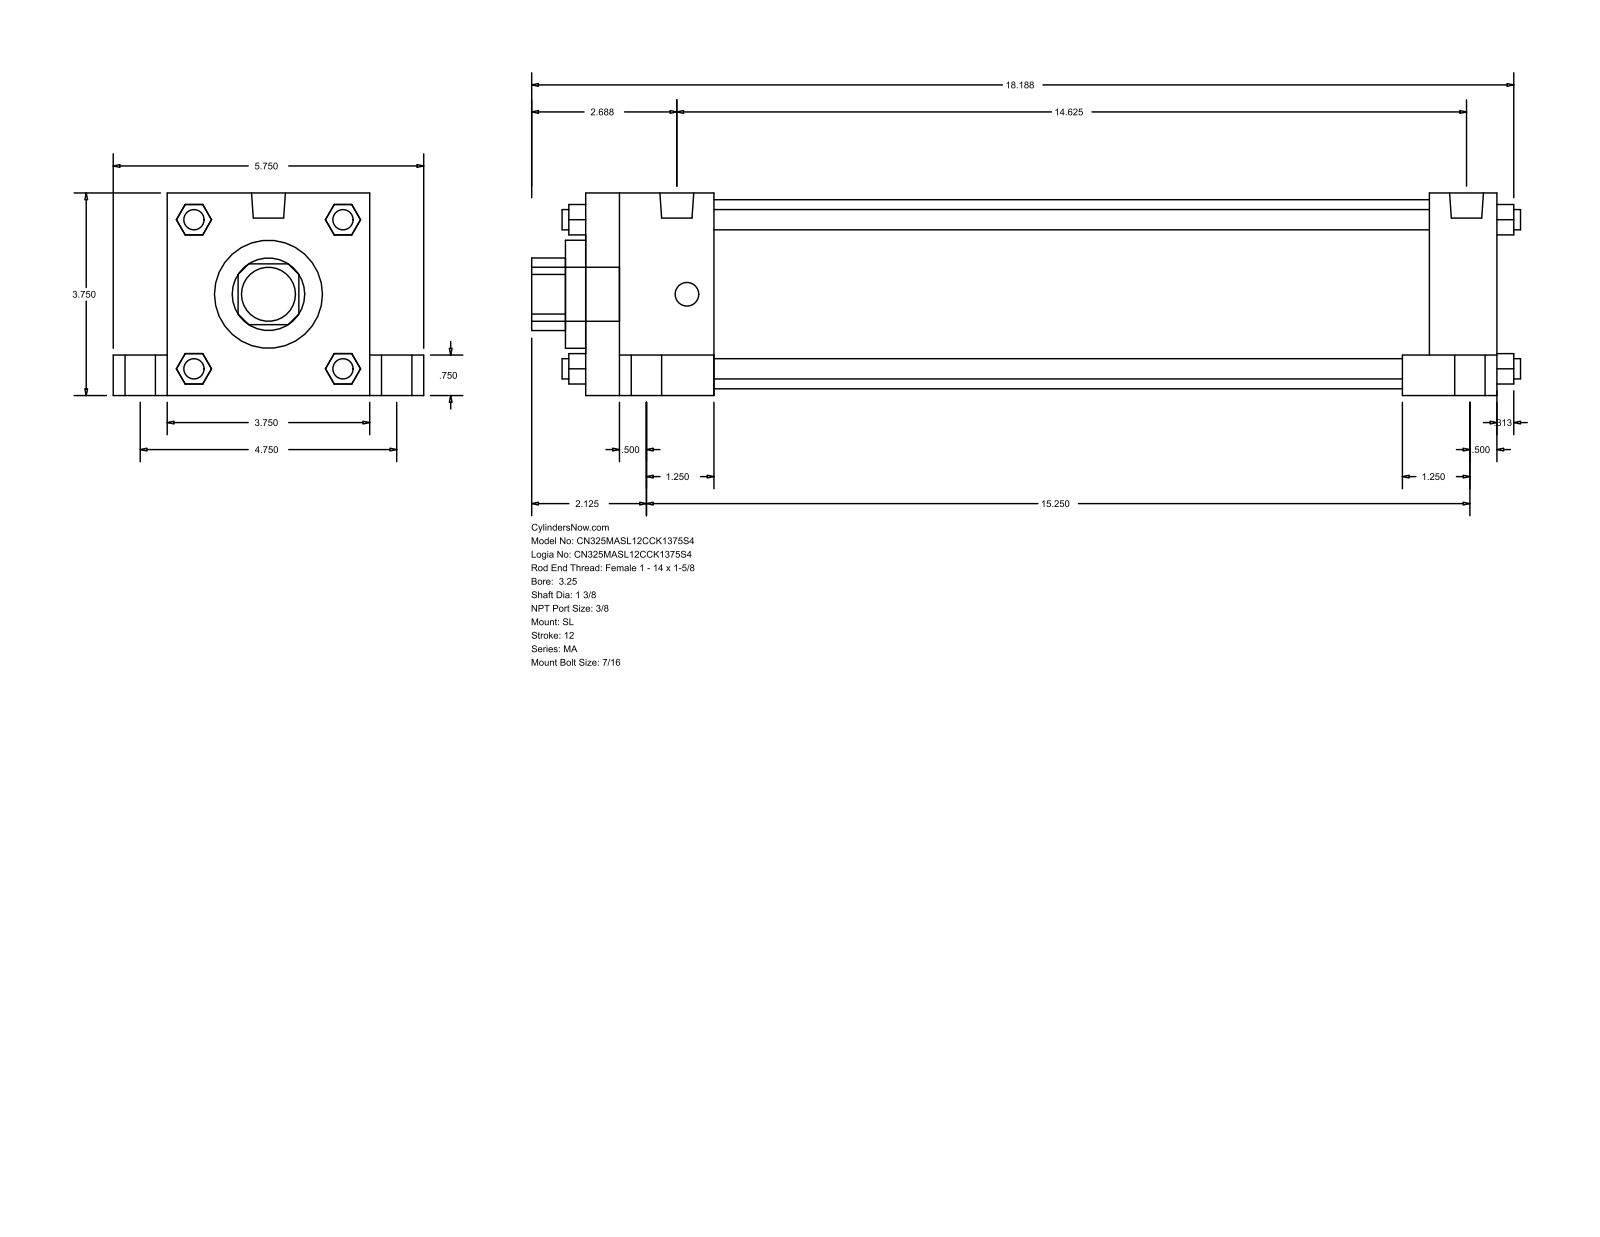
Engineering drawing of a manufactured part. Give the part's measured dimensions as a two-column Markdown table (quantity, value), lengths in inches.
| quantity | value |
| --- | --- |
| part name | MA_SL__0325_1.375 |
| STEP written by | GSSL Pune (CONFIG_CONTROL_DESIGN) |
| units | inches |
| bodies | 0 solids, 148 faces (112 planar, 36 cylindrical, 0 other) |
| overall size | 18.313 × 5.75 × 3.75 |
| round holes (diameter × count) | 1.375 × 1, 2 × 1, 3.5 × 1 |
| round bosses / shafts (diameter × count) | 0.813 × 4, 0.563 × 4, 0.437 × 4, 0.375 × 4, 0.627 × 2, 1 × 1 |
| partial cylindrical surfaces (radius × count) | 0.672 × 1 |
| main face-to-face distances | 3.75, 16.875, 13.25, 1, 4.75, 15.625, 1.25, 2.375, 14.5, 0.75 |
